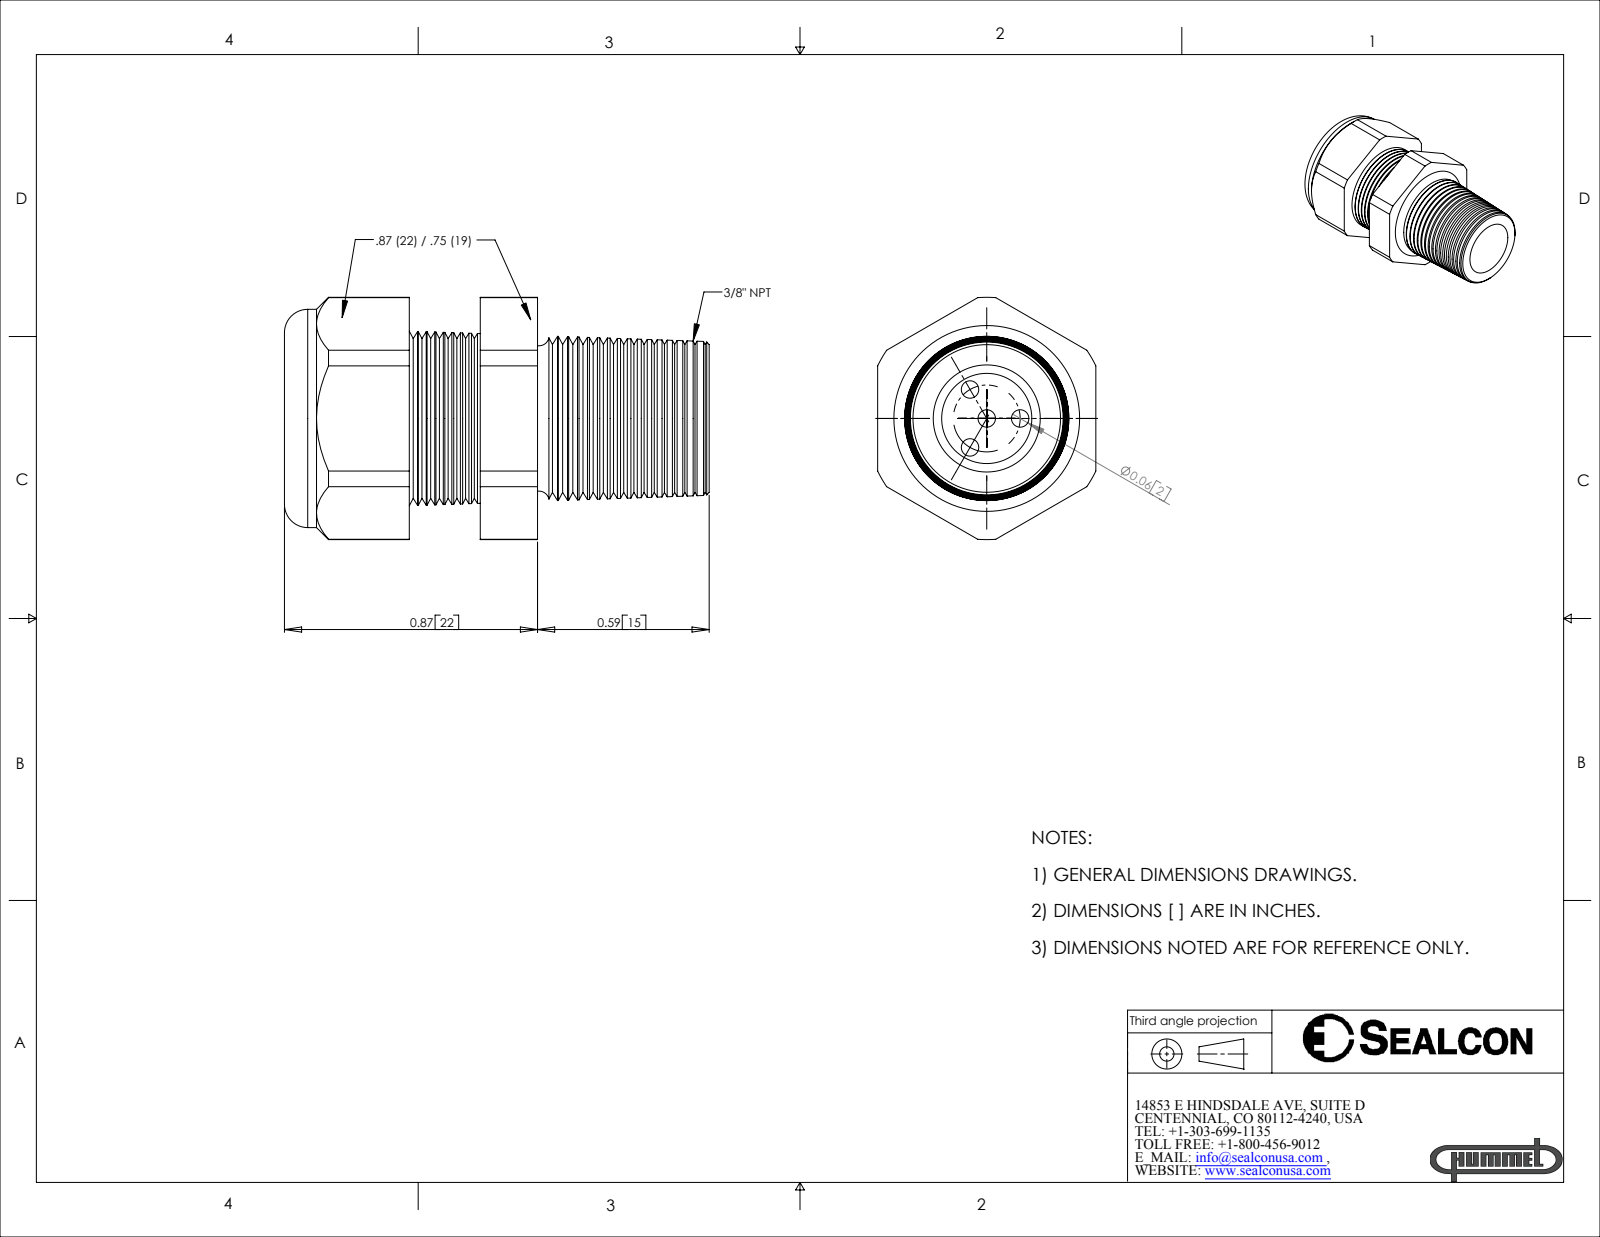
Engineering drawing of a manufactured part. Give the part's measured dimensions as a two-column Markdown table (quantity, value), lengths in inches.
| quantity | value |
| --- | --- |
| part name | CD09N1-GY |
| STEP written by | SolidWorks 2007 (CONFIG_CONTROL_DESIGN) |
| units | inches |
| bodies | 2 solids, 206 faces (20 planar, 28 cylindrical, 158 other) |
| overall size | 1.46 × 0.833 × 0.75 |
| volume | 0.369 in³ |
| surface area | 7.033 in² |
| round holes (diameter × count) | 0.06 × 4, 0.29 × 1, 0.31 × 1 |
| round bosses / shafts (diameter × count) | 0.75 × 1 |
| partial cylindrical surfaces (radius × count) | 0.416 × 1 |
| main face-to-face distances | 0.75, 0.673, 0.429, 0.244, 0.75, 0.87, 0.441, 0.197, 1.46, 1.031 |
| hole center spacings | 0.115, 0.199 |
